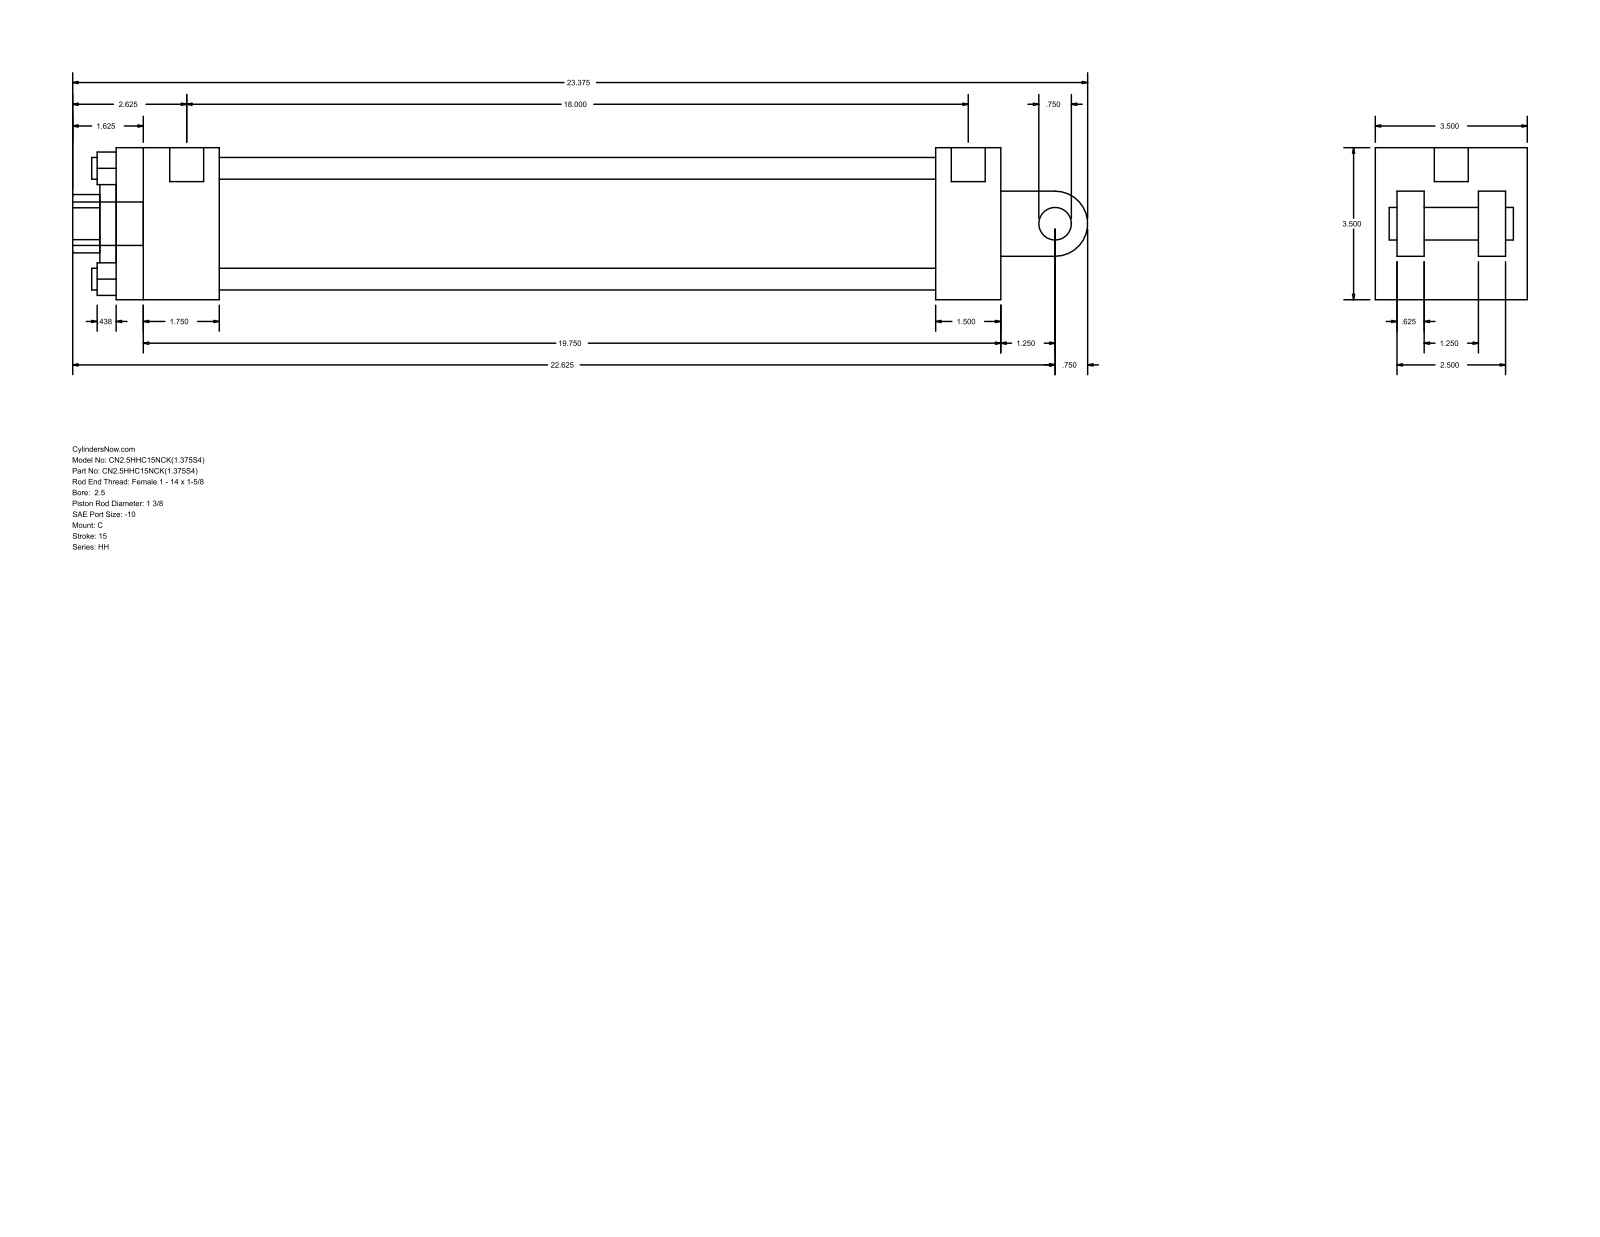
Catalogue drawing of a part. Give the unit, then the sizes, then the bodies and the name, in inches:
Units: inches
Overall size (bounding box): 23.375 × 3.5 × 3.5
Round holes (diameter × count): ⌀0.5 ×4, ⌀0.219 ×2, ⌀0.781 ×1, ⌀1.375 ×1, ⌀2 ×1, ⌀2.875 ×1
Round bosses / shafts (diameter × count): ⌀0.219 ×2, ⌀1 ×1, ⌀0.781 ×1, ⌀0.75 ×1
Partial cylindrical surfaces — rounded edges, fillets, slot ends (radius × count): R0.672 ×1, R0.75 ×1
Main face-to-face distances: 3.5, 20.375, 1.5, 2.5, 0.625, 0.5, 18.875, 2.375, 16.5, 18
Hole centre spacings: 1.803, 2.55, 3.606, 0.062
Bodies: 0 solids, 99 faces (70 planar, 29 cylindrical, 0 other)
Part name (STEP PRODUCT): HH_C__0250_1.375
STEP written by: GSSL Pune (CONFIG_CONTROL_DESIGN)
